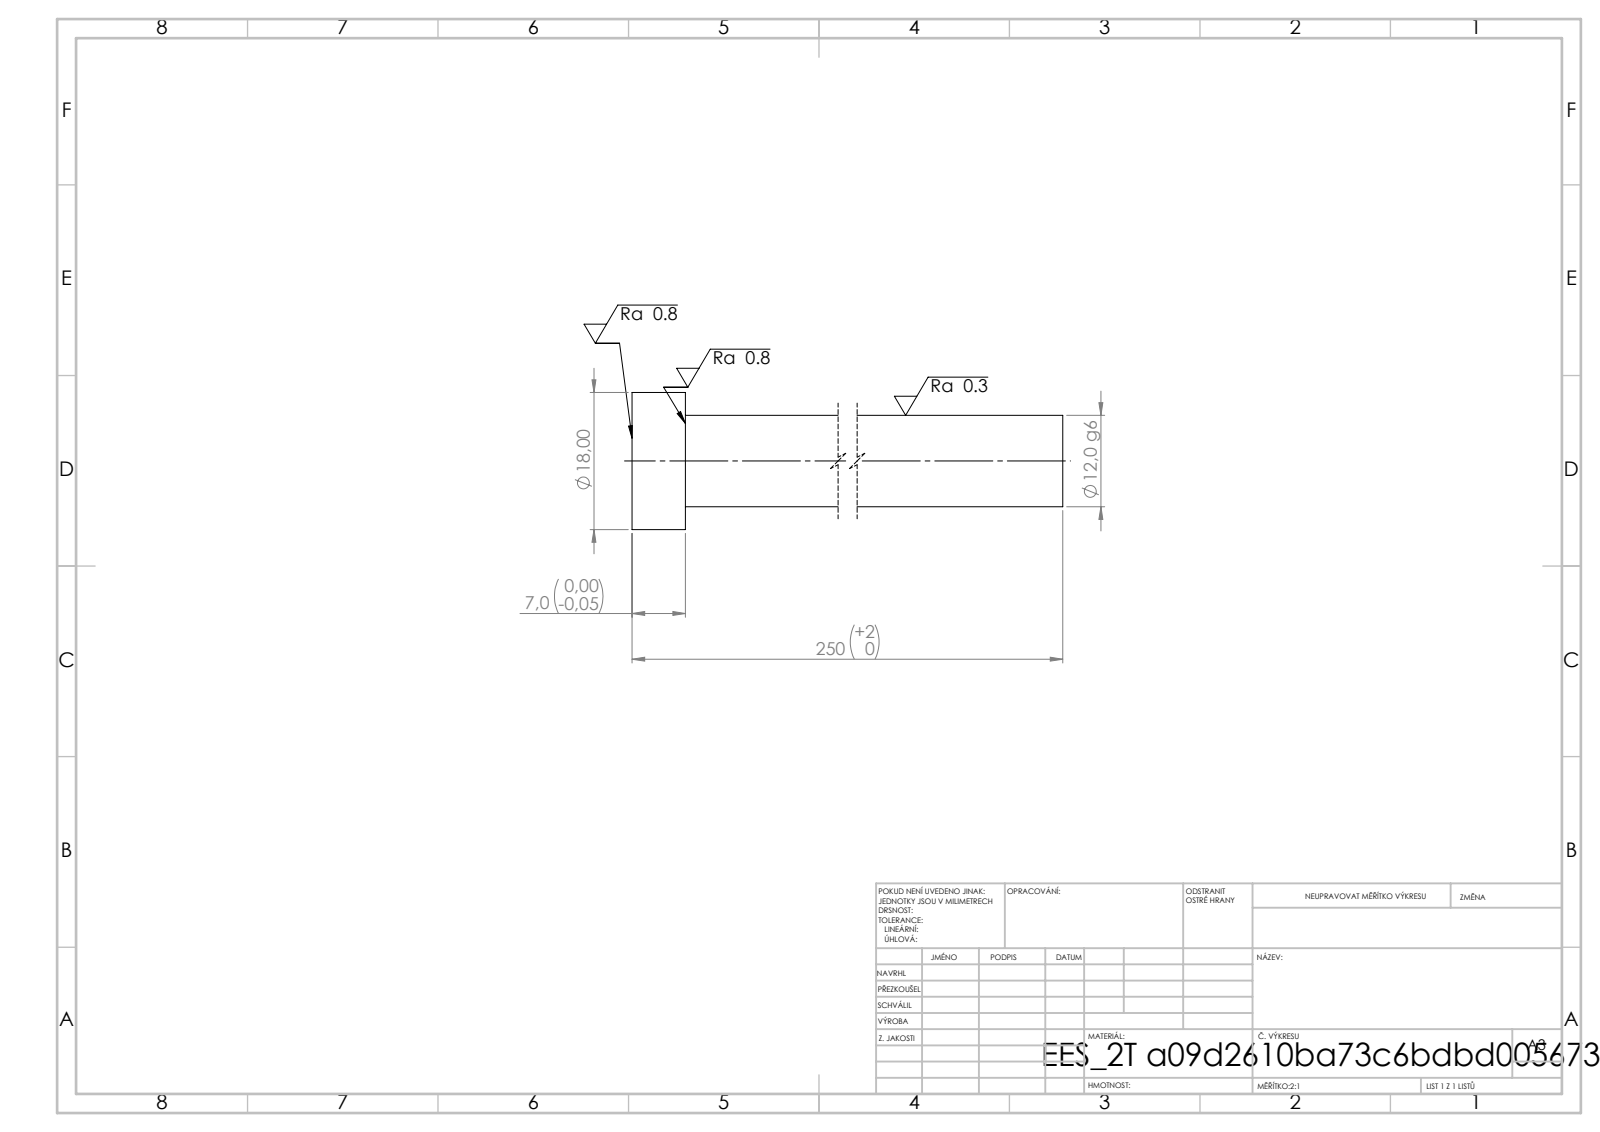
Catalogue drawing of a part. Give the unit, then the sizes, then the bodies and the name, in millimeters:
Units: millimetres
Overall size (bounding box): 250 × 18 × 18
Round bosses / shafts (diameter × count): ⌀18 ×1, ⌀12 ×1
Main face-to-face distances: 7, 250, 243
Volume: 29 264 mm³ · Surface area: 10 066 mm²
Bodies: 1 solid, 7 faces (3 planar, 4 cylindrical, 0 other)
STEP written by: SolidWorks 2019 (CONFIG_CONTROL_DESIGN)
